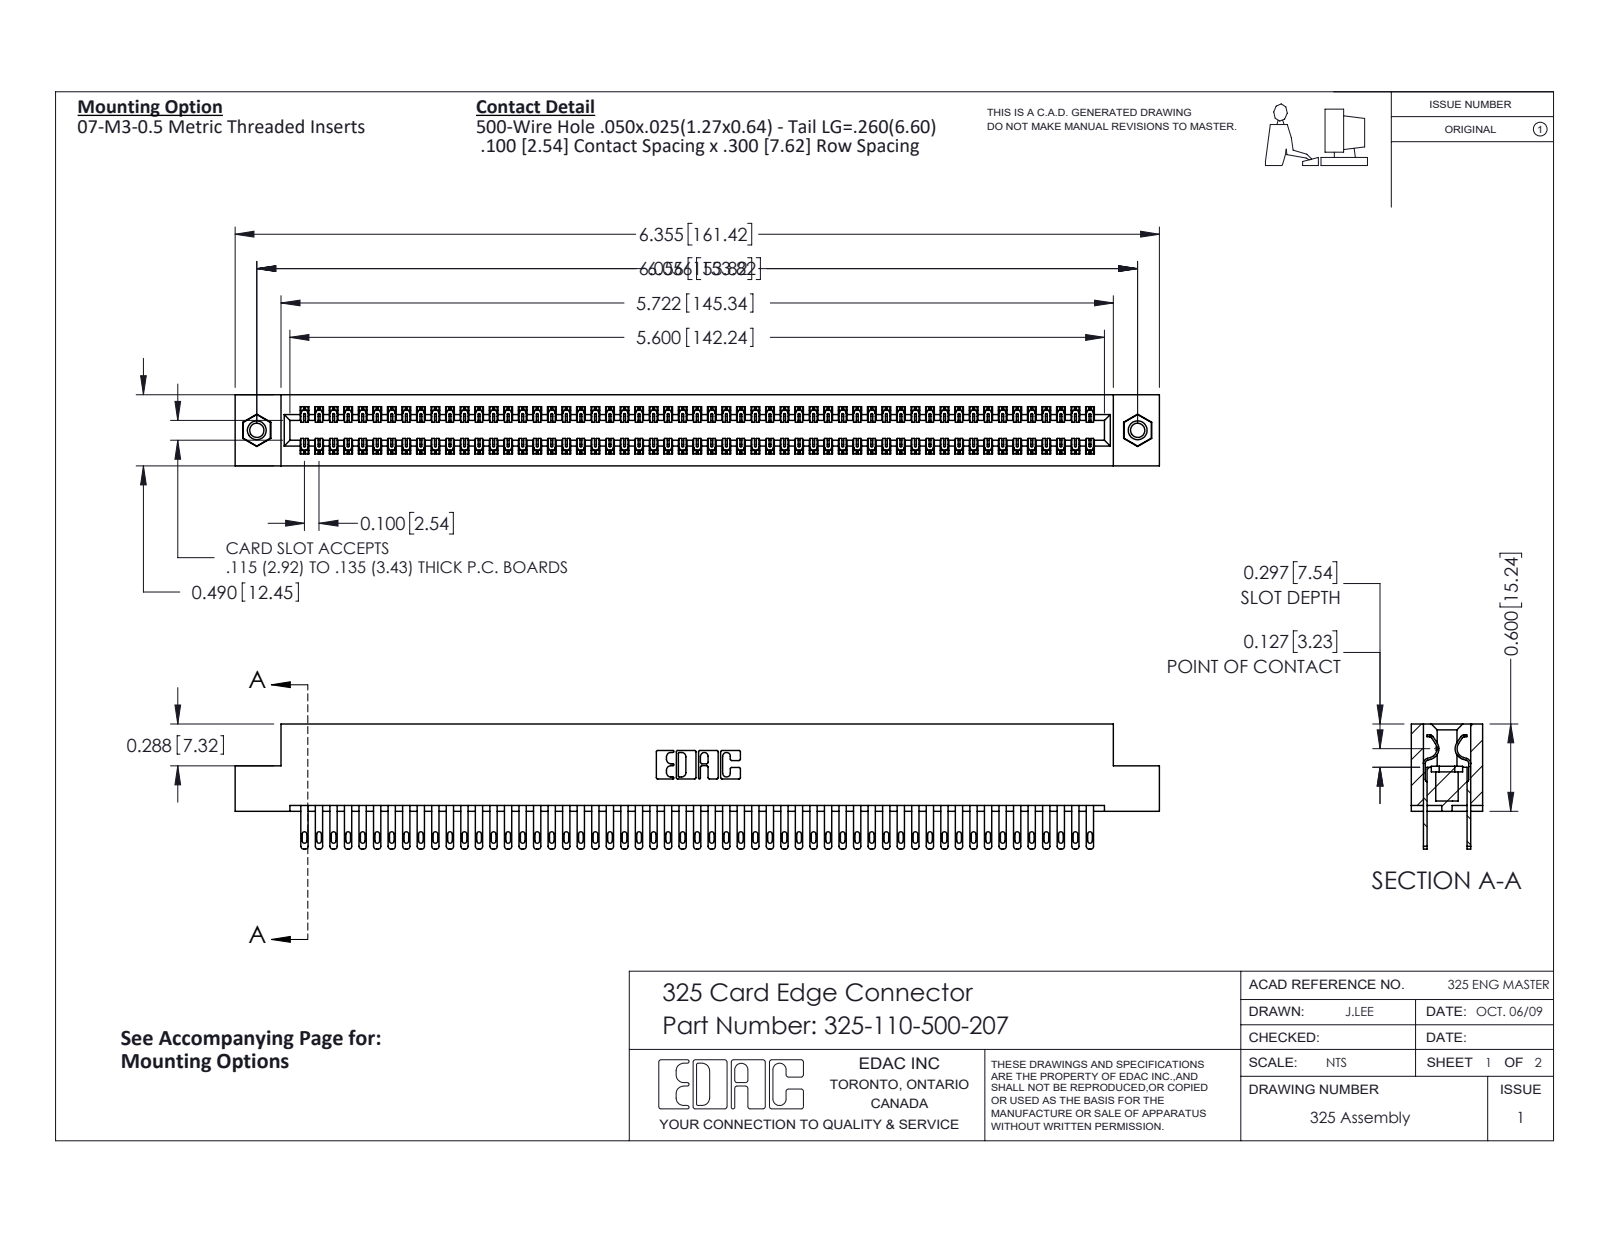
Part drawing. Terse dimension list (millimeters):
name: 325-292-001_325-293-100; 325-110-500-207; 325 Part_TI; 345-250-001_345-250-005-103
written by: SolidWorks 2016 (CONFIG_CONTROL_DESIGN)
unit: mm
bodies: 113 solids, 5454 faces (3402 planar, 2036 cylindrical, 16 other)
size: 161.4 × 21.8 × 12.4
volume: 21 270 mm³; area: 27 240 mm²
holes: 2× ⌀2.5, 2× ⌀3.2, 2× ⌀4.1
bosses: 2× ⌀3.9
rounds: 165× R0.2, 110× R0.4, 110× R0.5, 22× R0.3, 6× R0.2, 6× R0.8, 3× R0.7, 2× R0.4
face distances: 2.1, 10.3, 7.6, 2.7, 9.7, 0.6, 12.4, 8.3, 7, 6.7
hole spacings: 153.8
